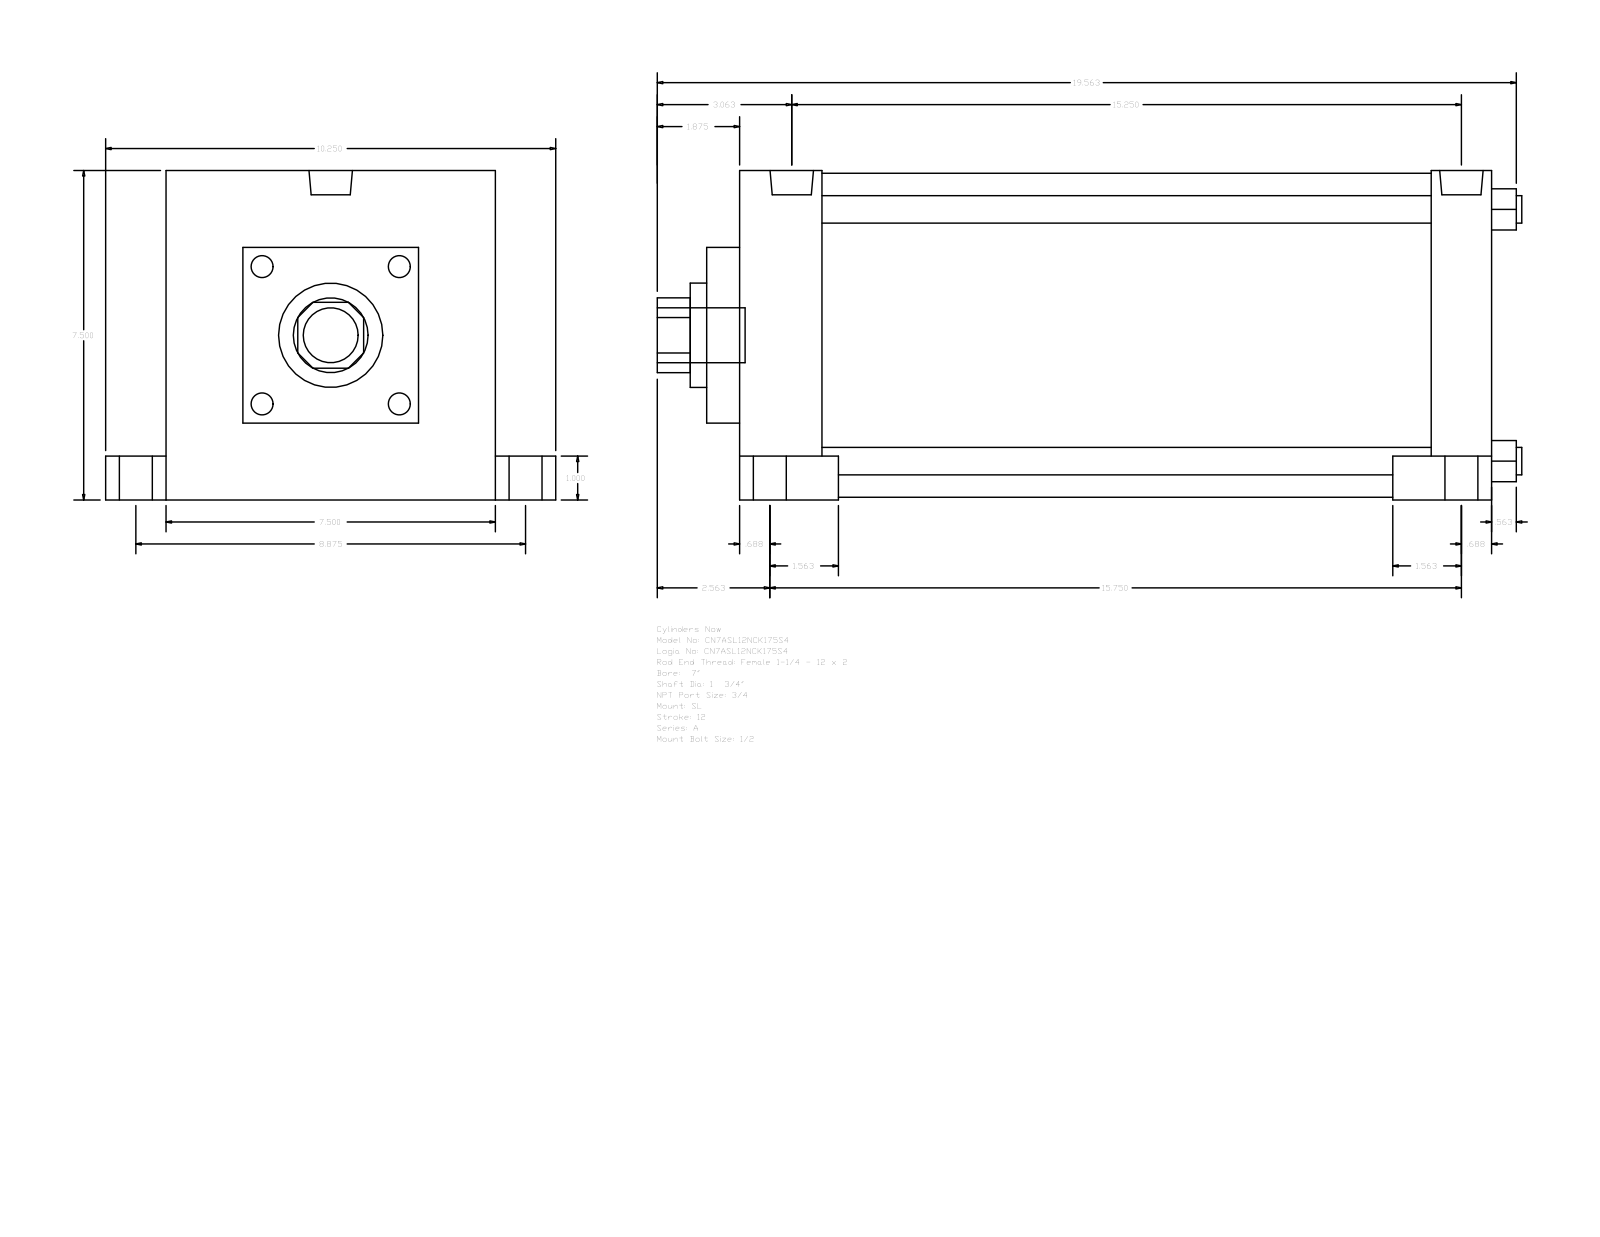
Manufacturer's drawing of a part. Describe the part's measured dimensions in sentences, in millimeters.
The part is named "A_SL__0700_1.75". Its 3-D file was written by "GSSL Pune (CONFIG_CONTROL_DESIGN)". It is 0 solids with 117 faces: 85 planar, 32 cylindrical and 0 other. Overall it measures 500.06 by 260.35 by 190.5 millimeters. Round holes: 4 of diameter 15.88, 1 of diameter 44.45, 1 of diameter 60.33, 1 of diameter 187.32. Round bosses or shafts: 4 of diameter 25.4, 4 of diameter 19.05, 4 of diameter 15.08, 2 of diameter 25.12, 1 of diameter 31.75. Partial cylindrical surfaces (rounded edges, fillets, slot ends): 1 of radius 21.63. The main face-to-face distances are 190.5, 434.98, 19.05, 44.45, 34.92, 47.63, 387.35, 400.06, 352.43, 146.05. The hole center spacings are 102.91, 145.54, 205.82.
